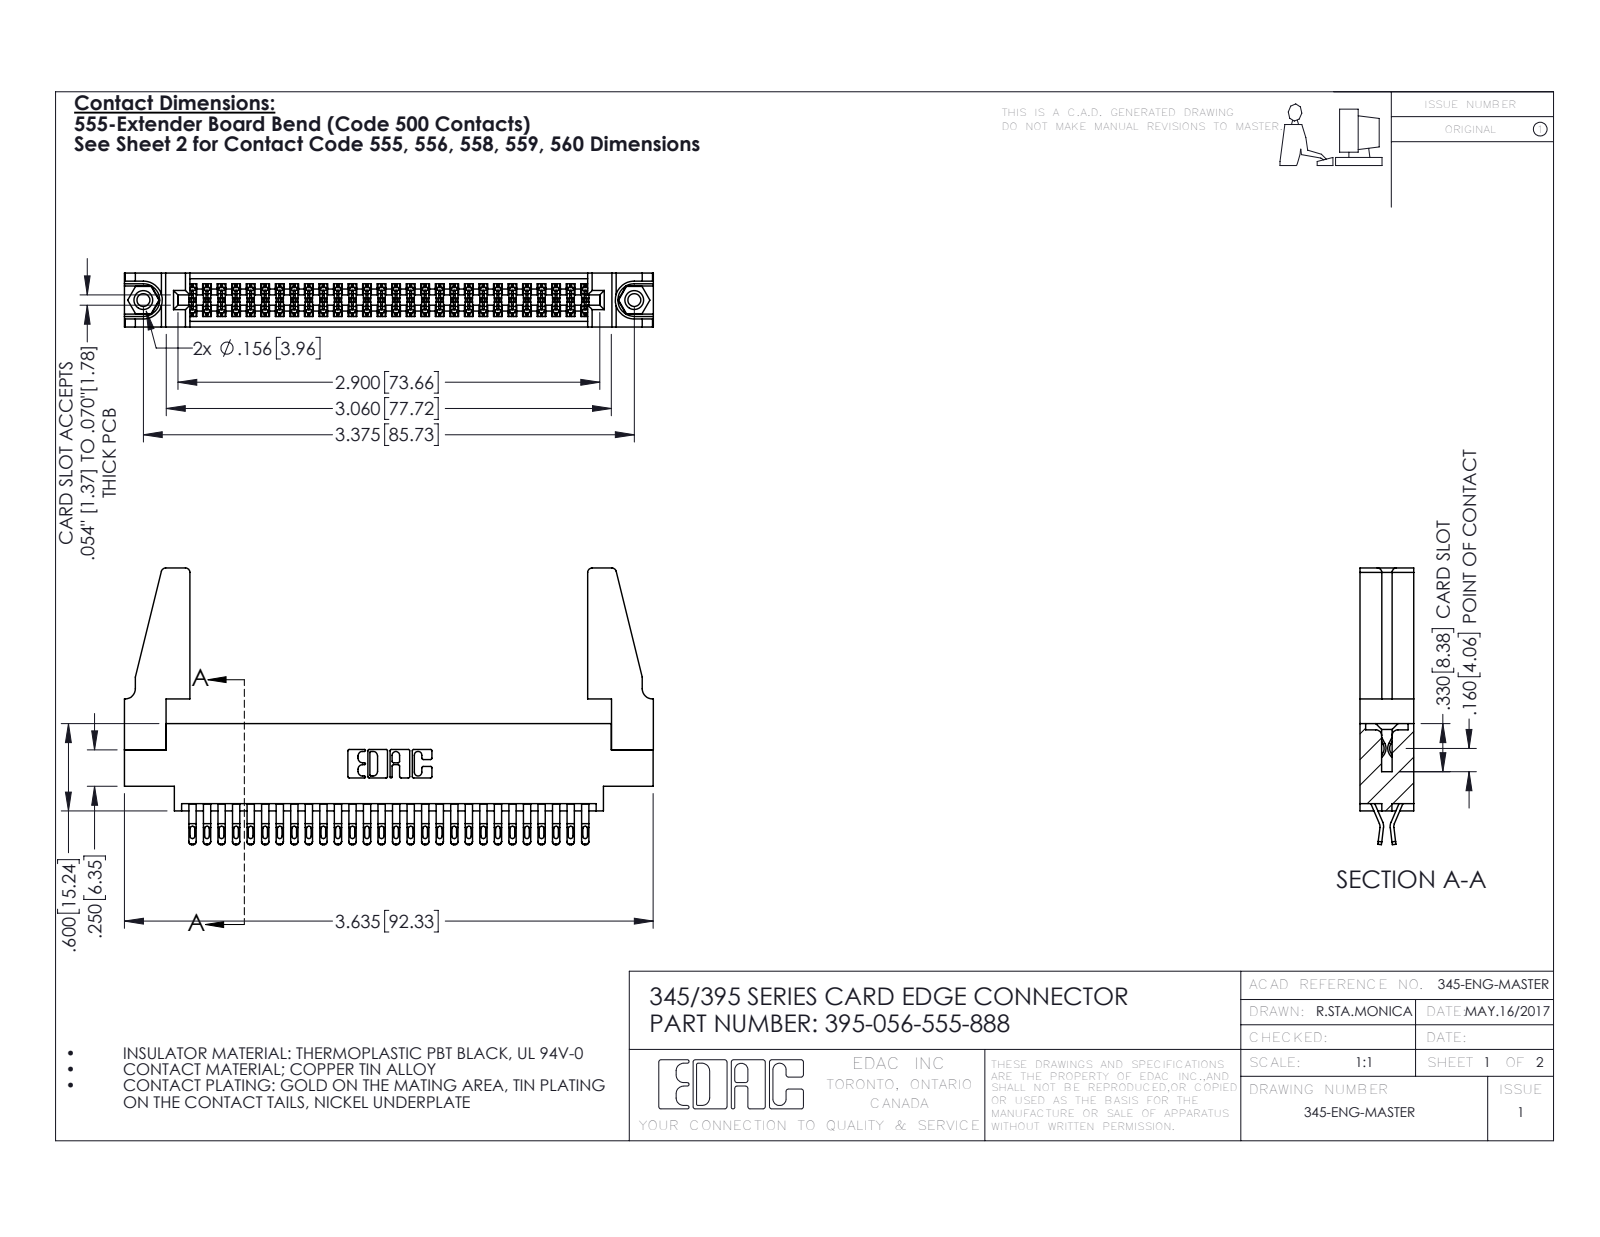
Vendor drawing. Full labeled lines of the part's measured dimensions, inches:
Part name (STEP PRODUCT): 345-250-001_345-250-001-102; 345 Part_0.170 Offset - 0.156 Dia-TH; 345-292-001_555 Tail; 395-056-555-888 (+1 more)
STEP written by: SolidWorks 2016 (CONFIG_CONTROL_DESIGN)
Units: inches
Bodies: 61 solids, 3390 faces (1892 planar, 1482 cylindrical, 16 other)
Overall size (bounding box): 3.636 × 1.902 × 0.37
Volume: 0.741 in³ · Surface area: 25.89 in²
Round holes (diameter × count): ⌀0.089 ×2, ⌀0.125 ×2, ⌀0.156 ×2, ⌀0.064 ×1
Round bosses / shafts (diameter × count): ⌀0.155 ×2
Partial cylindrical surfaces — rounded edges, fillets, slot ends (radius × count): R0.016 ×140, R0.02 ×112, R0.006 ×84, R0.01 ×22, R0.03 ×8, R0.007 ×6, R0.031 ×6, R0.026 ×3
Main face-to-face distances: 0.37, 0.072, 0.298, 0.025, 0.098, 0.272, 0.2, 0.225, 0.175, 0.149
Hole centre spacings: 0.27, 3.14, 3.375
